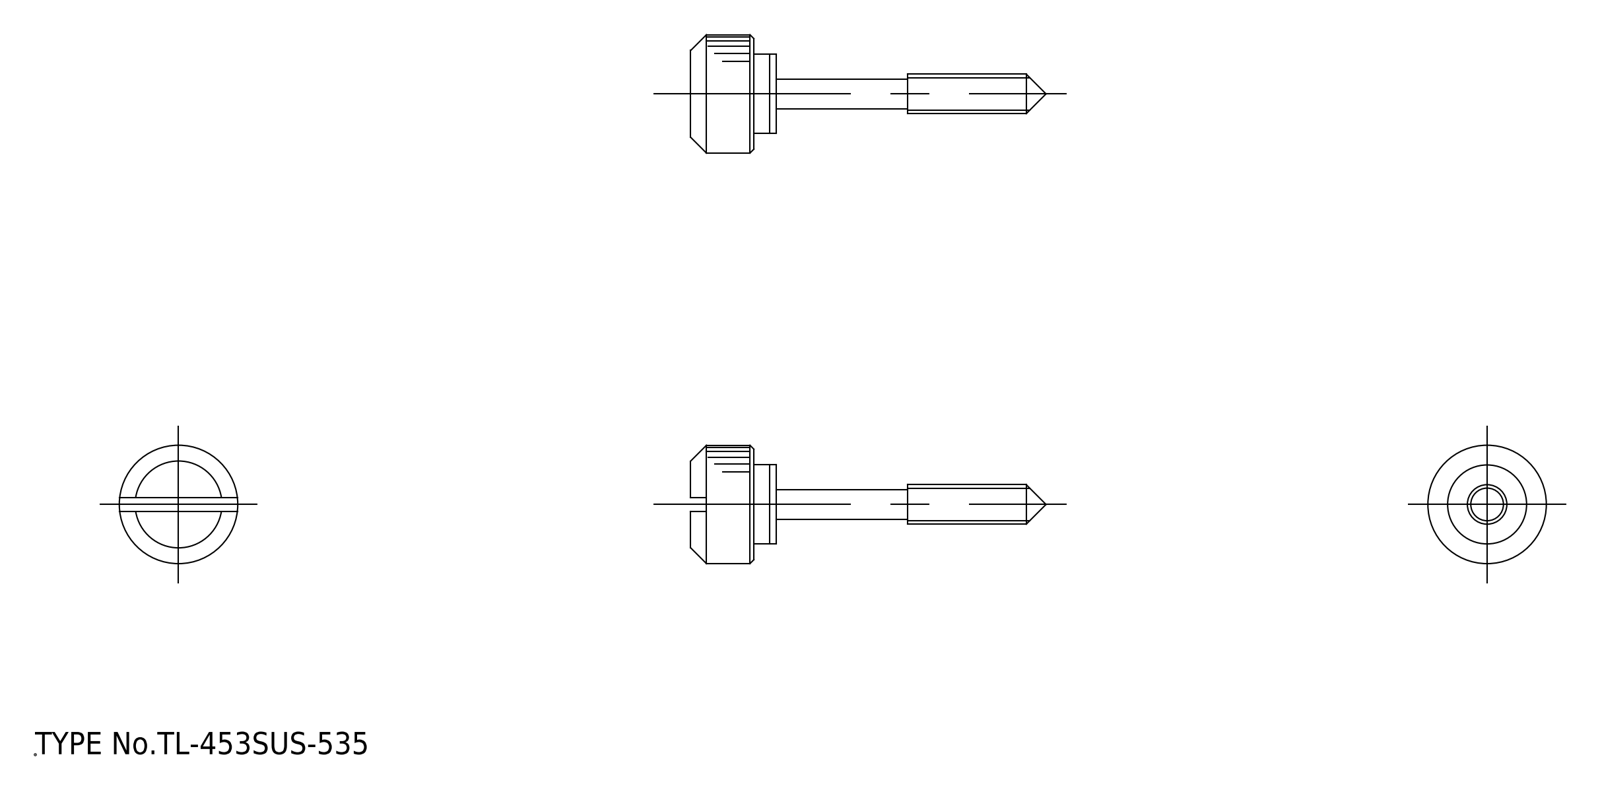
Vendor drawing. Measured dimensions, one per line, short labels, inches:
name: washer; knob
written by: spGate 19.8.4 (****-****-****-****) (AUTOMOTIVE_DESIGN)
unit: in
bodies: 2 solids, 42 faces (18 planar, 18 cylindrical, 6 other)
size: 1.772 × 0.591 × 0.591
volume: 0.121 in³; area: 2.167 in²
bosses: 1× ⌀0.591, 1× ⌀0.394, 1× ⌀0.197, 1× ⌀0.15
rounds: 4× R0.031, 1× R0.077
face distances: 0.079, 0.315, 0.394, 0.425, 0.11, 0.031, 0.236, 0.346, 0.071, 1.083
